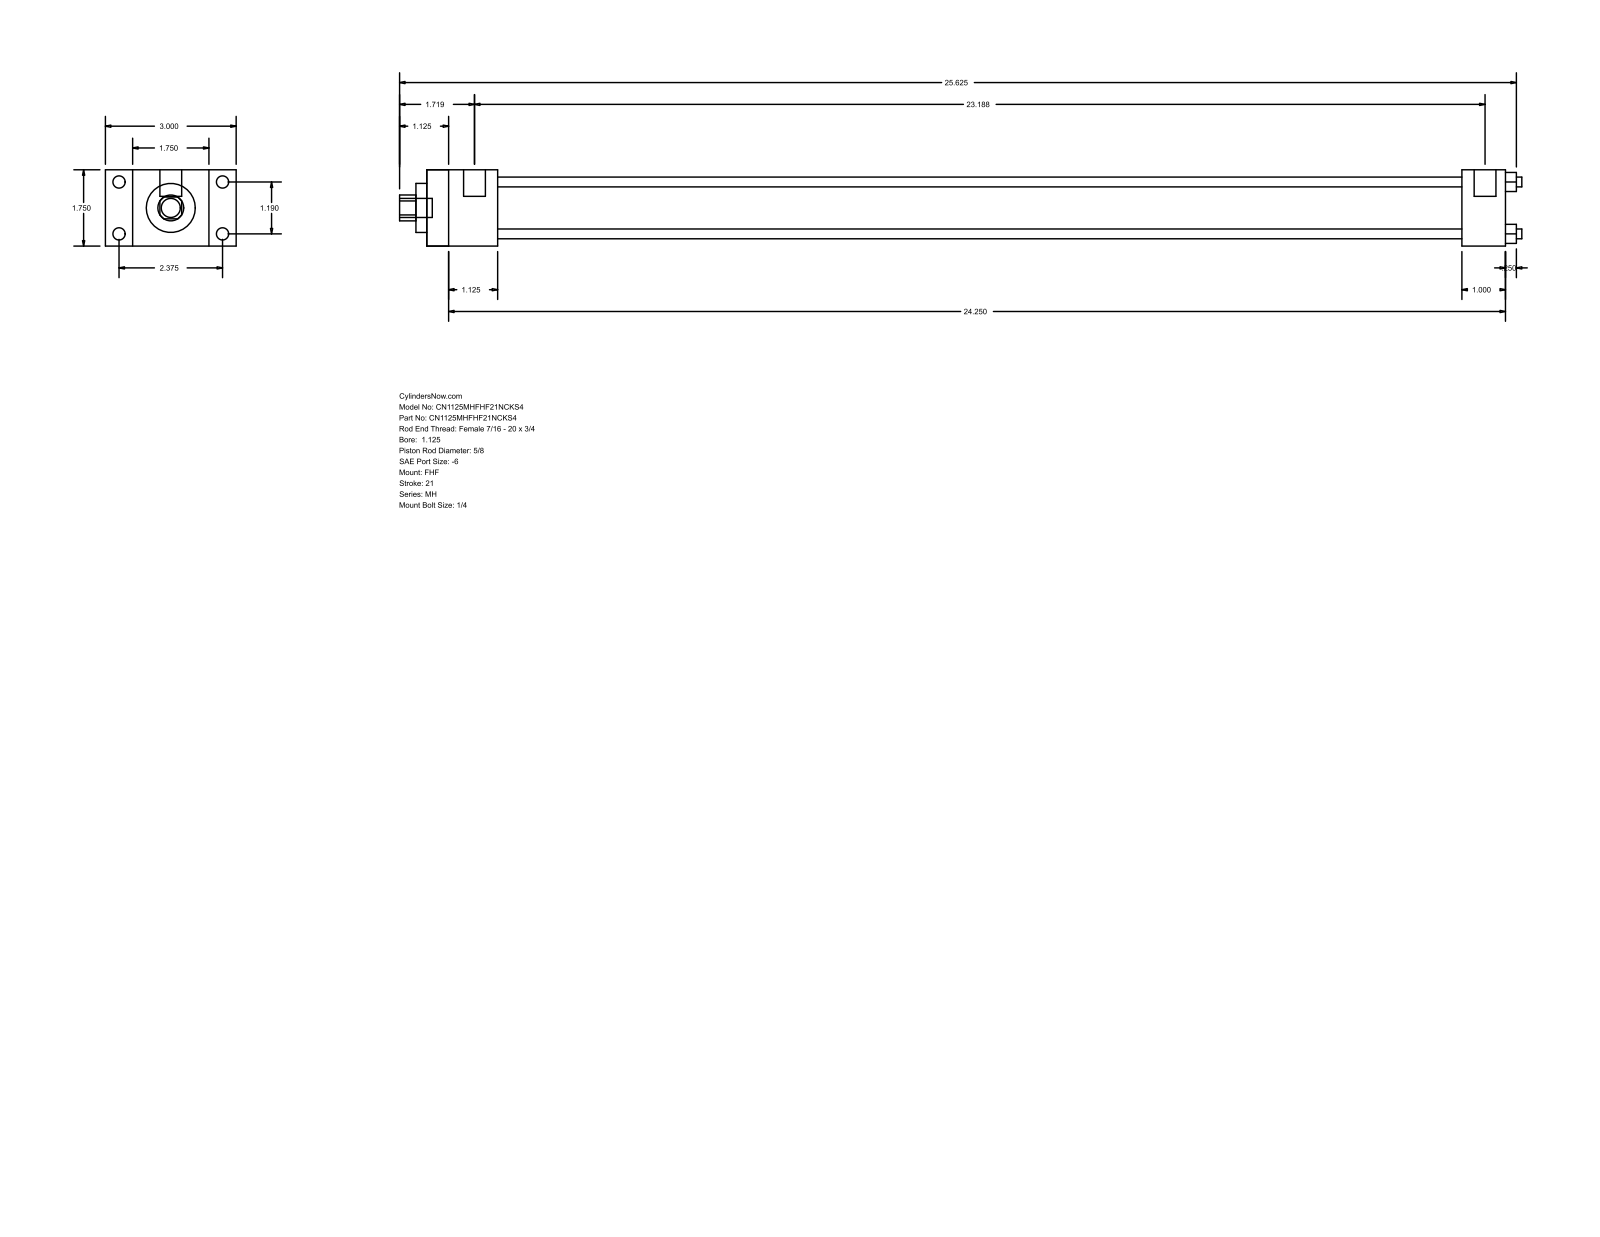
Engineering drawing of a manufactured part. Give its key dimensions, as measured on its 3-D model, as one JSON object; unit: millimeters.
{"part_name": "MH_FHF__0112_0.625", "step_written_by": "GSSL Pune (CONFIG_CONTROL_DESIGN)", "units": "millimeters", "bodies": {"solids": 0, "faces": 88, "planar": 60, "cylindrical": 28, "other": 0}, "overall_size": [654.05, 76.2, 44.45], "round_holes": [[5.71, 4], [15.88, 1], [28.57, 1], [34.92, 1]], "round_bosses_or_shafts": [[7.14, 4], [5.56, 4], [12.7, 2], [11.11, 1]], "partial_cylinders_radius": [[7.54, 1]], "face_to_face_distances": [44.46, 15.87, 60.33, 41.27, 76.2, 628.64, 587.37, 603.24, 561.97, 25.4], "hole_center_spacings": [21.37, 30.22, 42.74]}
